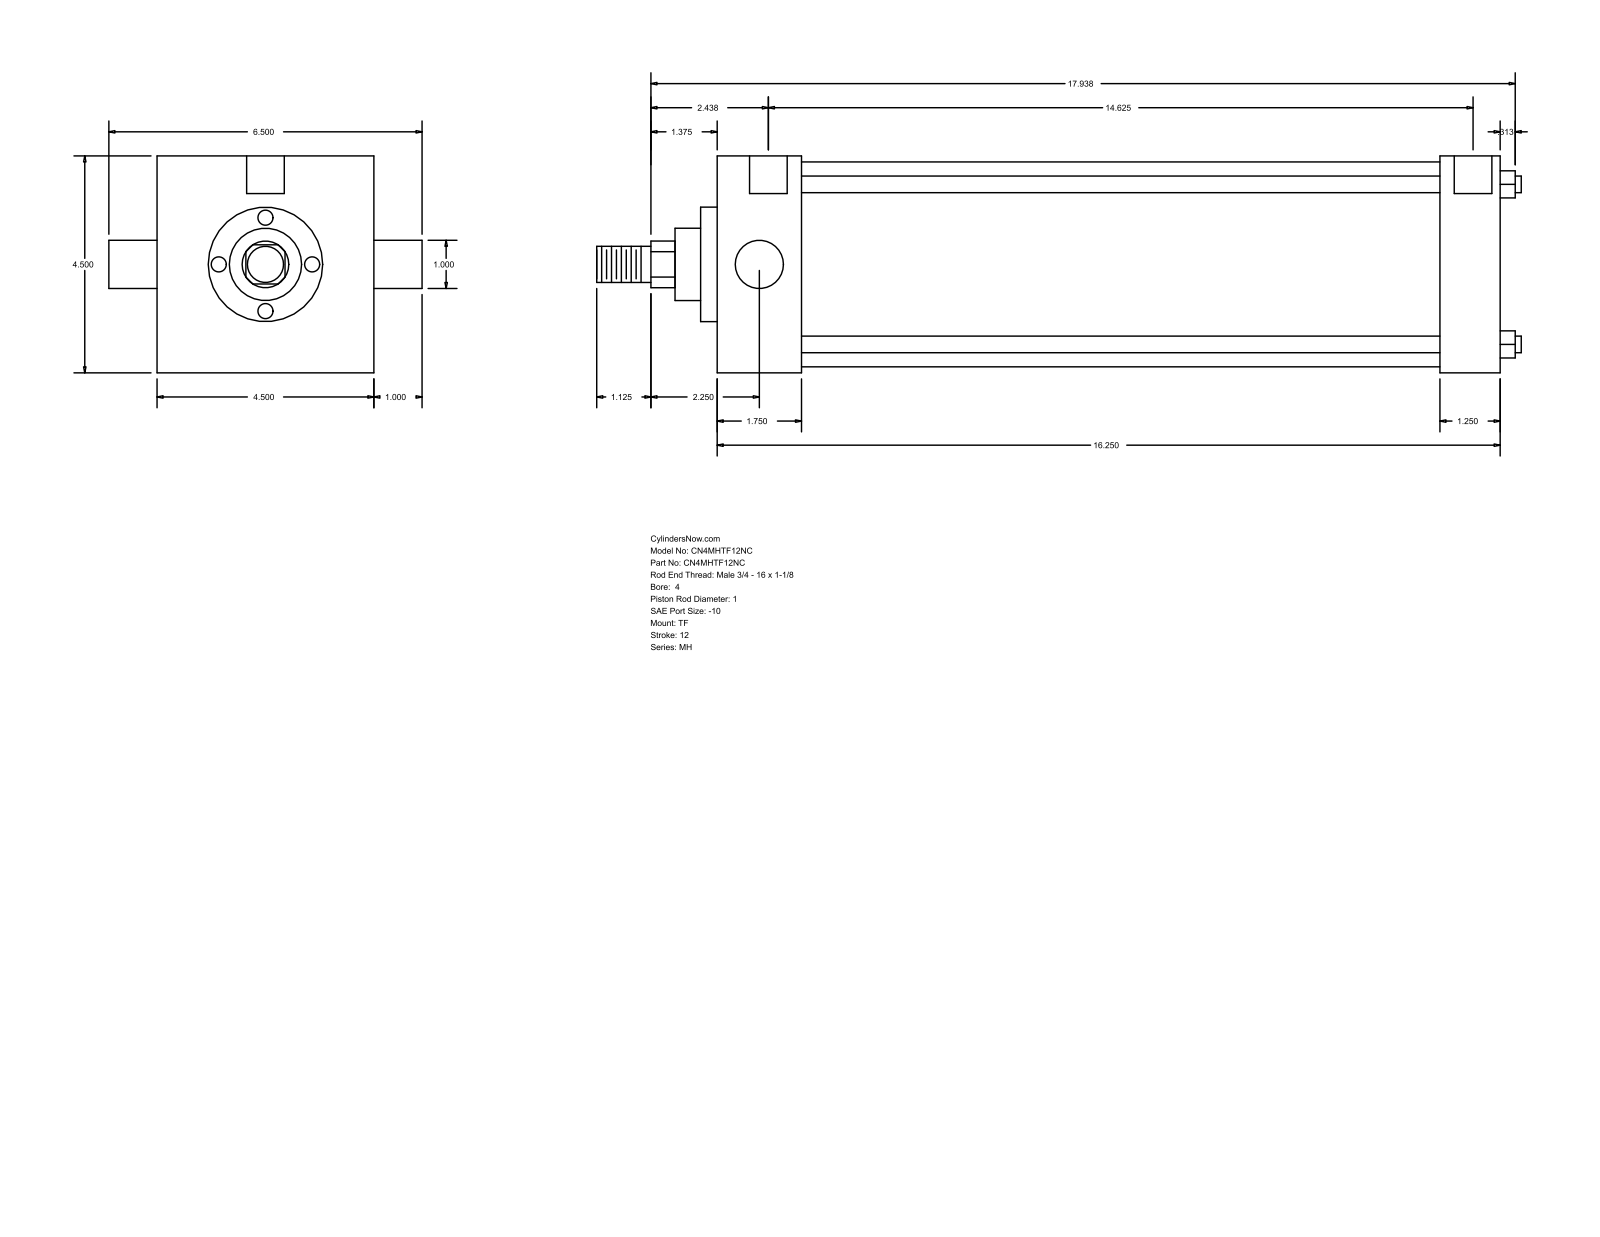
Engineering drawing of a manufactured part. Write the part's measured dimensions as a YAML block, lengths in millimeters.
part_name: "MH_TF__0400_1"
step_written_by: "GSSL Pune (CONFIG_CONTROL_DESIGN)"
units: millimeters
bodies: {solids: 0, faces: 86, planar: 61, cylindrical: 25, other: 0}
overall_size: [487.36, 165.1, 114.3]
round_holes:
  - {diameter: 8.73, count: 3}
  - {diameter: 19.84, count: 2}
round_bosses_or_shafts:
  - {diameter: 8.76, count: 4}
  - {diameter: 25.4, count: 2}
  - {diameter: 107.95, count: 1}
  - {diameter: 60.33, count: 1}
  - {diameter: 38.1, count: 1}
  - {diameter: 19.05, count: 1}
partial_cylinders:
  - {radius: 12.29, count: 1}
face_to_face_distances: [114.3, 412.76, 44.46, 368.3, 381.01, 336.55, 31.75, 8.73, 53.19, 389.74]
hole_center_spacings: [1.58, 1.59, 371.48, 373.06, 373.07, 374.65]
